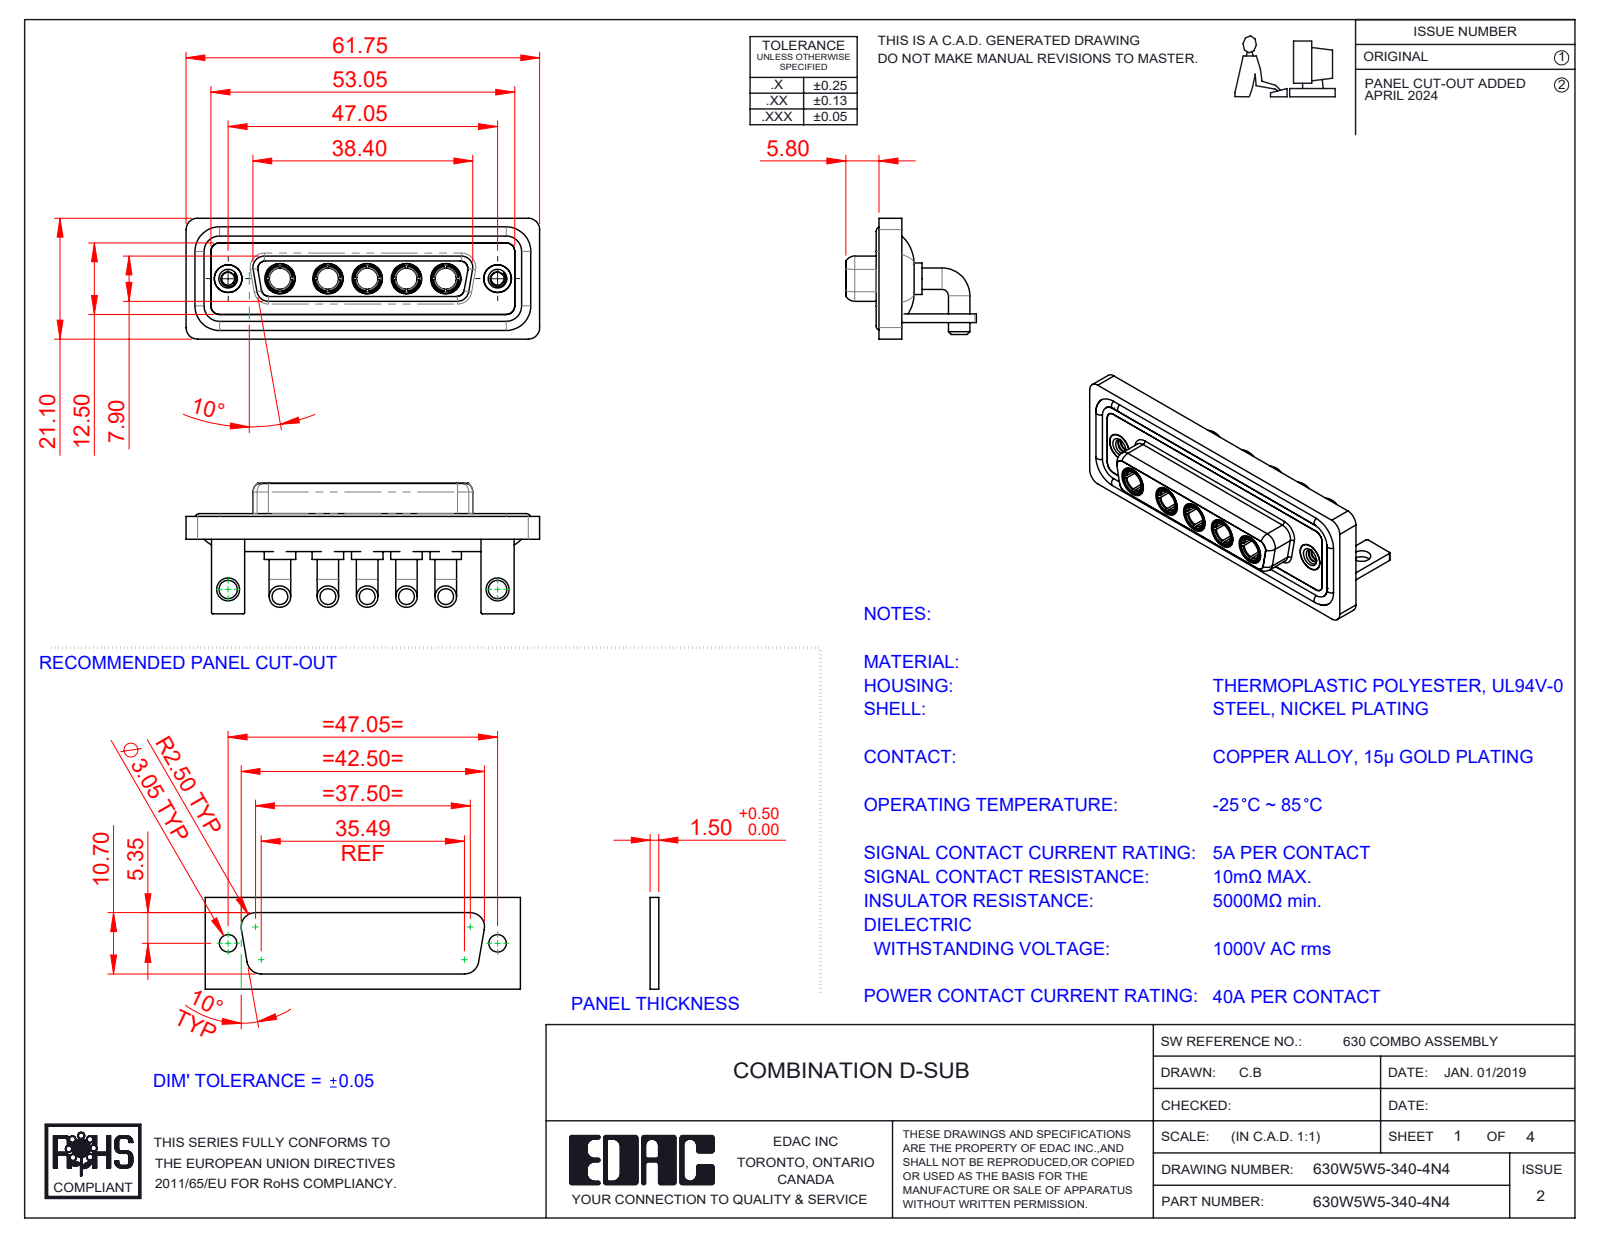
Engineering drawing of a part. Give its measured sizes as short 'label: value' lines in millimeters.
name: 630Combo Stabilizer Bracket_50 Contacts; 630W5W5-340-4N4; 630Combo Housing_5W5; Power Socket_40A RA (+4 more)
written by: SolidWorks 2023 (CONFIG_CONTROL_DESIGN)
unit: mm
bodies: 19 solids, 824 faces (270 planar, 337 cylindrical, 217 other)
size: 61.75 × 22.8 × 21.1
volume: 9 165 mm³; area: 14 767 mm²
holes: 7× ⌀4.85, 5× ⌀3.7, 5× ⌀5.3, 2× ⌀2.26, 2× ⌀3.2, 2× ⌀4, 2× ⌀4.05, 2× ⌀5
bosses: 10× ⌀3.75, 5× ⌀5.5, 5× ⌀5.2, 5× ⌀4.96, 5× ⌀4.75, 4× ⌀1.6, 2× ⌀4.95, 2× ⌀4.8
rounds: 19× R2, 18× R1.5, 16× R0.25, 8× R1.35, 8× R1.6, 5× R0.5, 5× R2.1, 4× R0.6
face distances: 0.4, 1.8, 2.9, 3.7, 1.5, 4.1, 1.1, 1.4, 1.6, 2.5
hole spacings: 6.86, 9.04, 38.01, 47.05, 6.87, 8.38, 13.72, 13.73
